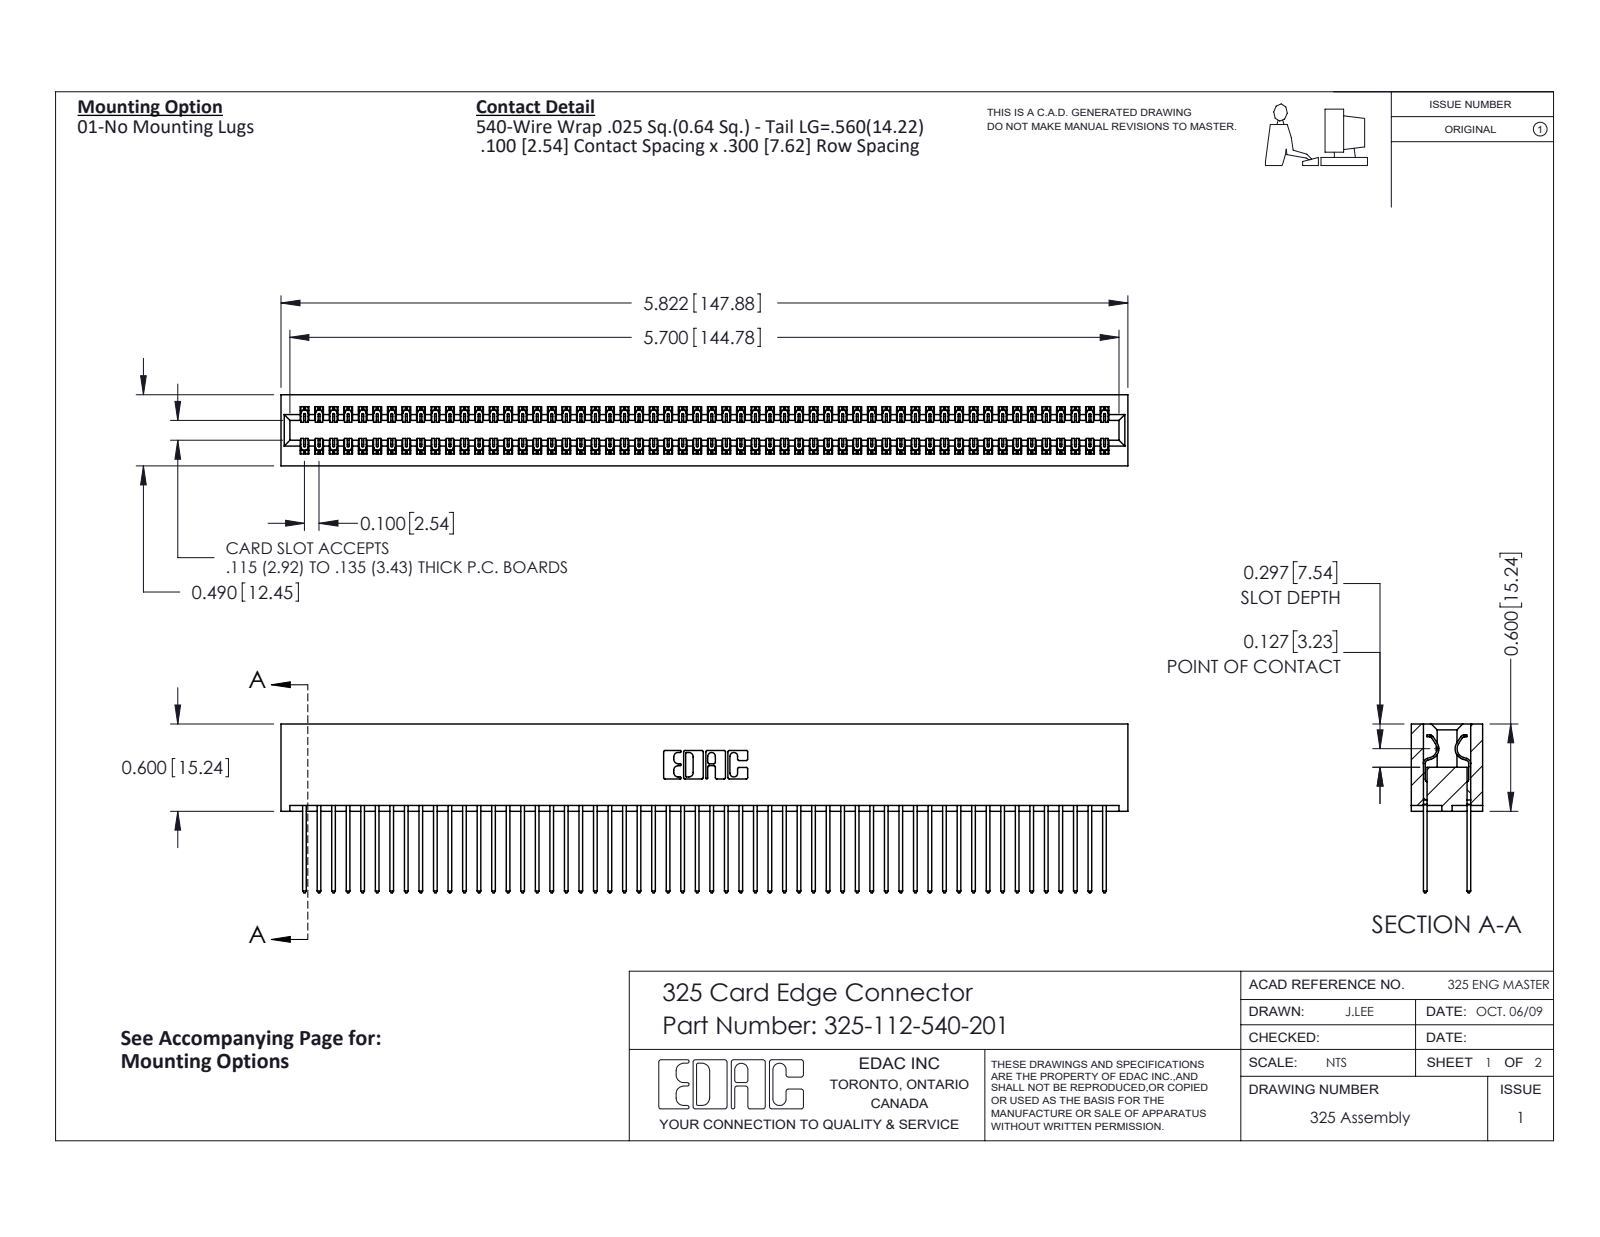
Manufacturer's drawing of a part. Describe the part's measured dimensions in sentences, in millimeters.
The part is named "325-112-540-201; 325 Part_Lugless; 325-292-001_325-293-140". Its 3-D file was written by "SolidWorks 2016 (CONFIG_CONTROL_DESIGN)". It is 113 solids with 5930 faces: 4098 planar, 1832 cylindrical and 0 other. Overall it measures 147.9 by 29.5 by 12.4 millimeters. Its volume is 20 250 cubic millimeters and its surface area 27 520 square millimeters. Partial cylindrical surfaces (rounded edges, fillets, slot ends): 168 of radius 0.2, 112 of radius 0.3, 22 of radius 0.3, 6 of radius 0.2, 6 of radius 0.8, 3 of radius 0.7, 2 of radius 0.4, 2 of radius 0.6. The main face-to-face distances are 2.1, 10.3, 7.6, 2.7, 9.7, 0.6, 8.3, 12.4, 7, 14.2.
